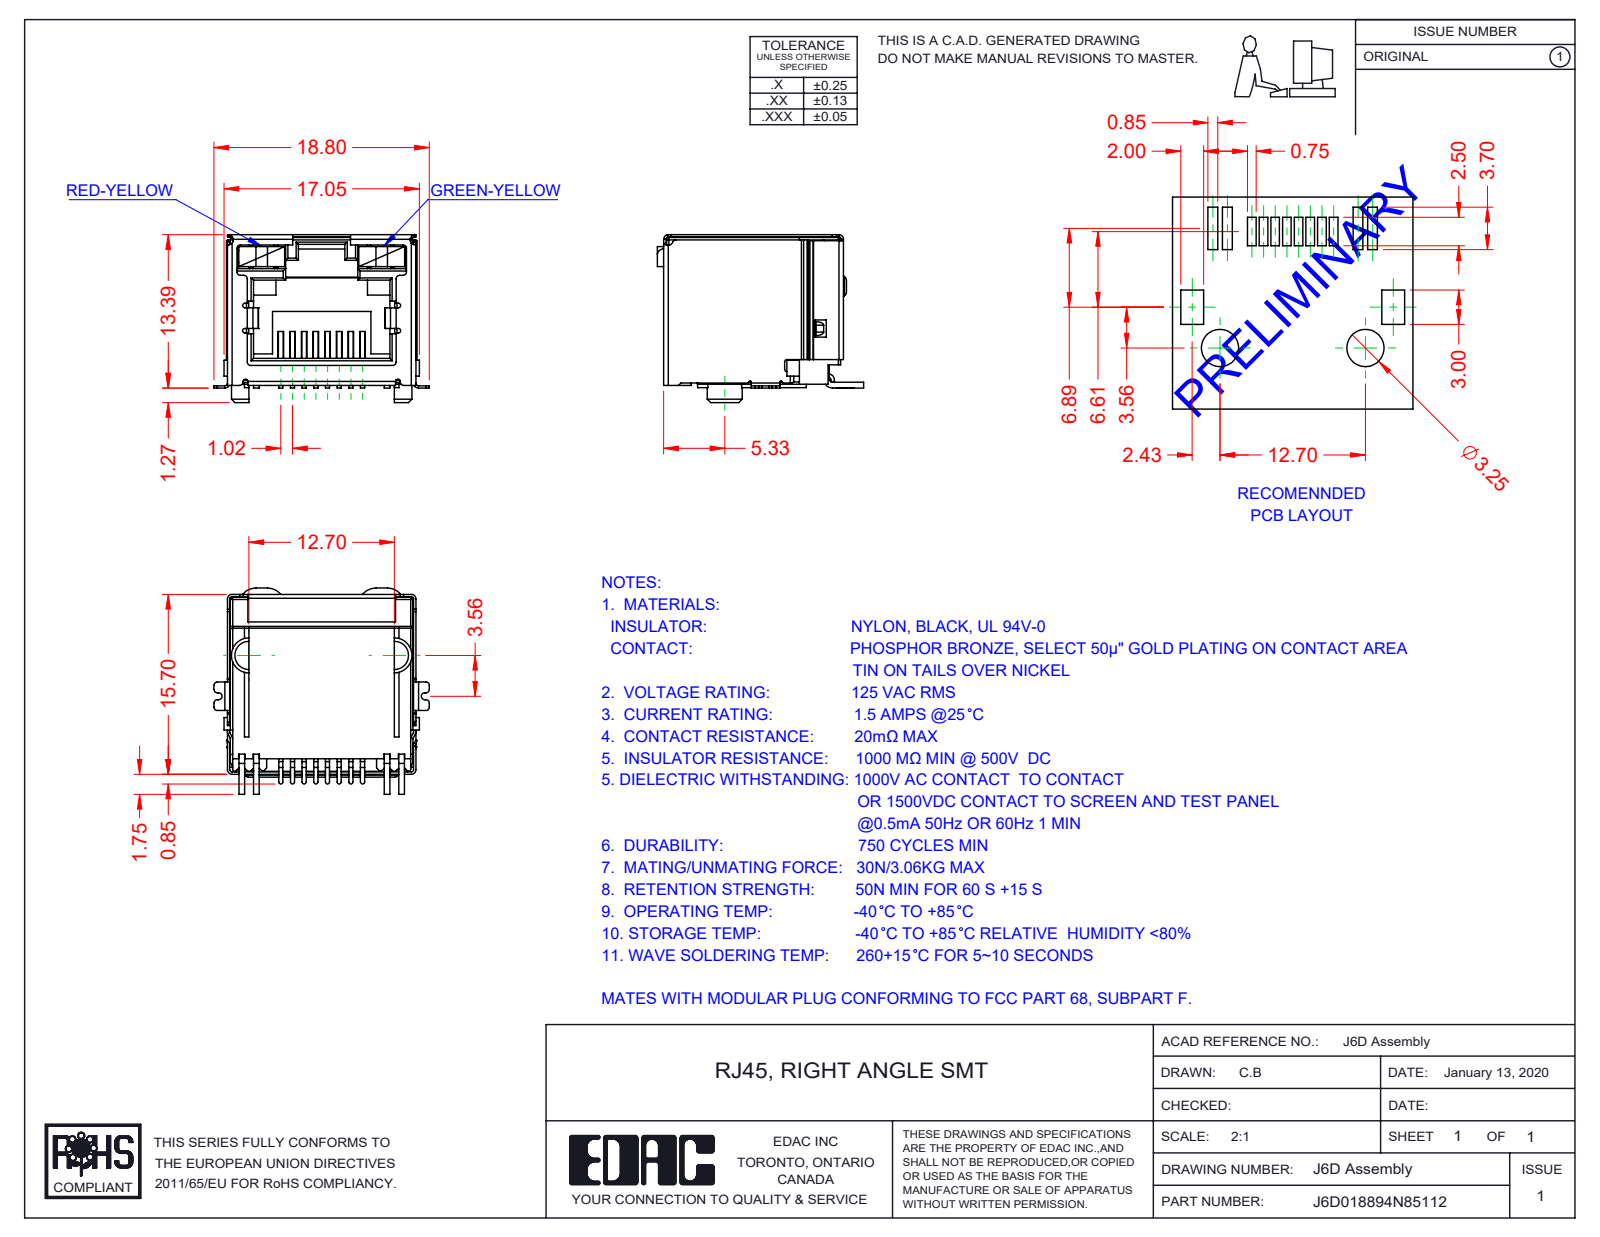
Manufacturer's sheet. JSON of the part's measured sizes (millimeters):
{"part_name": "6D Insulator; 6D Contacts; 6D LED RH_5-Green-Yellow; 6D Shield_LED - No EMI (+2 more)", "step_written_by": "SolidWorks 2016 (CONFIG_CONTROL_DESIGN)", "units": "millimeters", "bodies": {"solids": 12, "faces": 899, "planar": 646, "cylindrical": 220, "other": 33}, "overall_size": [18.8, 18, 14.65], "volume_mm3": 1804, "surface_area_mm2": 4898, "partial_cylinders_radius": [[0.3, 39], [0.2, 37], [0.4, 16], [0.1, 12], [0.15, 8], [0.18, 8], [0.5, 6], [1.5, 5]], "face_to_face_distances": [16, 16.25, 16.2, 2.25, 1, 15.95, 16.05, 12.8, 0.45, 16.45]}
